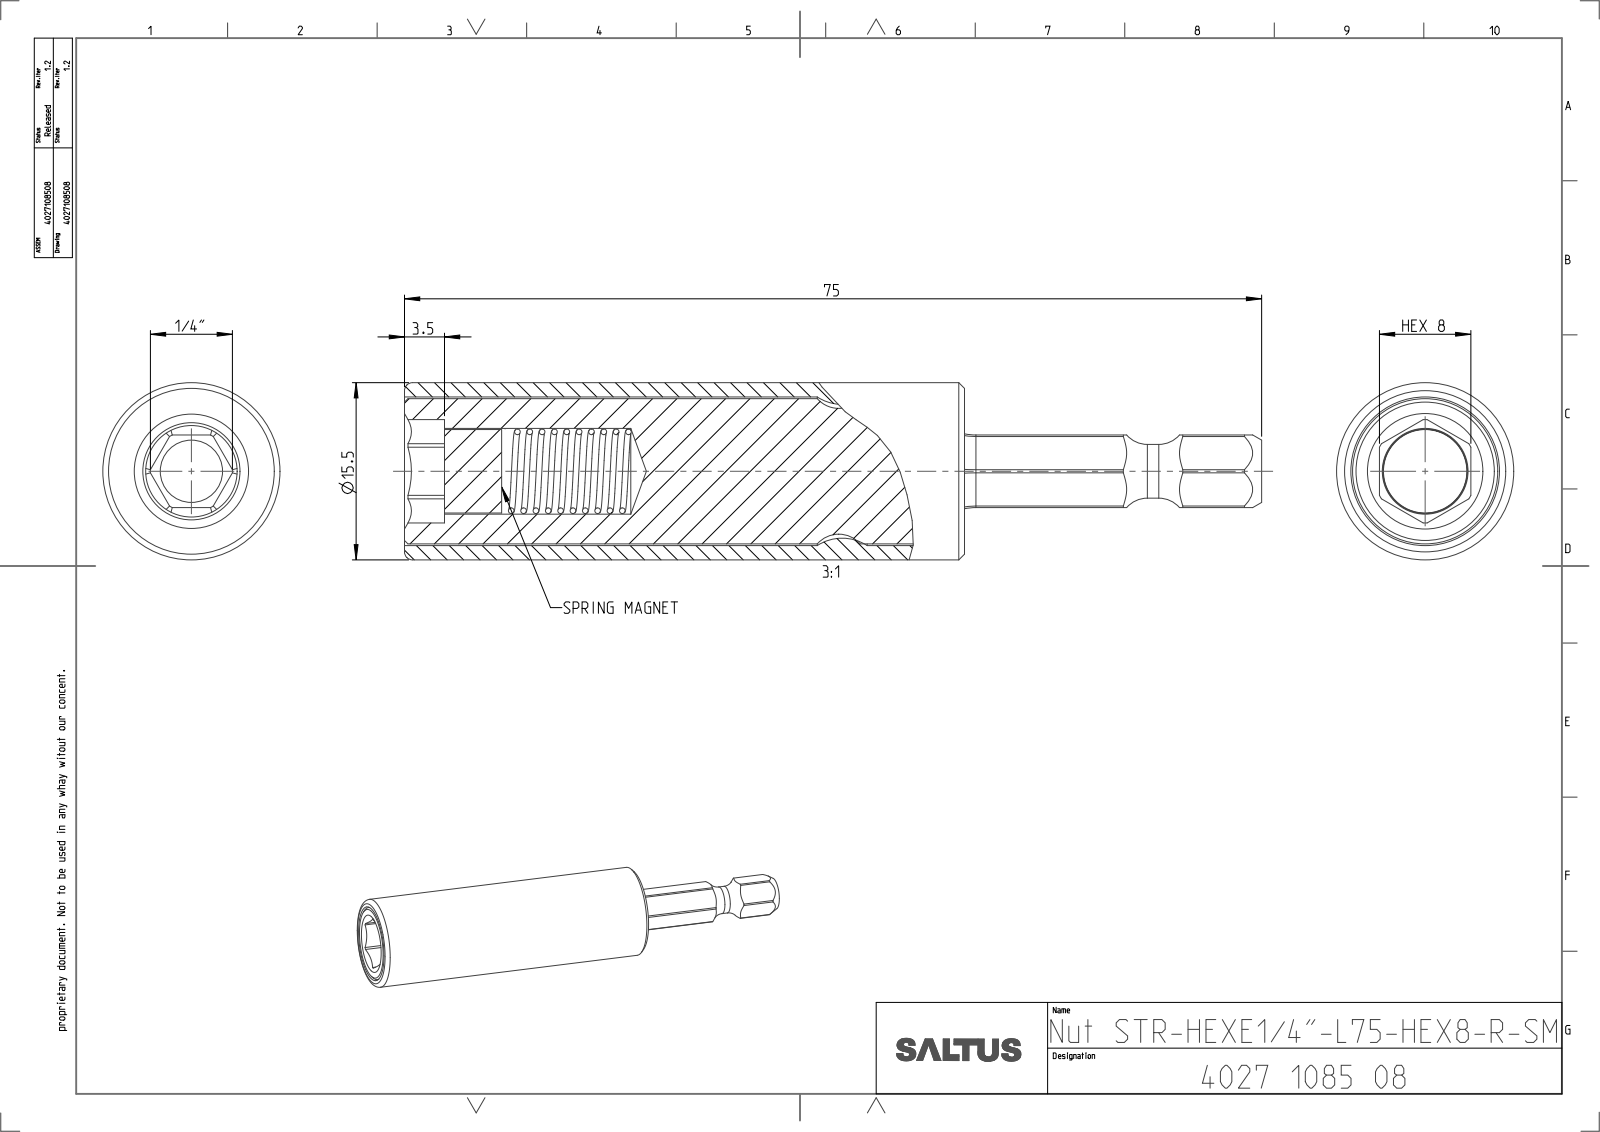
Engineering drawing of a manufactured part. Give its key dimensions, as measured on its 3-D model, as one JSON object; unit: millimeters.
{"part_name": "4027903088; 4027299024; 4027108508_ASM", "step_written_by": "CREO PARAMETRIC BY PTC INC, 2022414 (CONFIG_CONTROL_DESIGN)", "units": "millimeters", "bodies": {"solids": 4, "faces": 112, "planar": 28, "cylindrical": 44, "other": 40}, "overall_size": [75, 15.5, 15.5], "volume_mm3": 8868, "surface_area_mm2": 8212, "round_holes": [[7.5, 1], [10, 1], [13, 1]], "round_bosses_or_shafts": [[15.5, 1], [12.7, 1], [8, 1], [7.3, 1], [4.7, 1]], "partial_cylinders_radius": [[5, 6], [3.59, 1], [4.52, 1]], "face_to_face_distances": [6.34, 6.36, 49, 45.5, 3.5, 40.5, 5, 8.5, 8, 1.25]}
